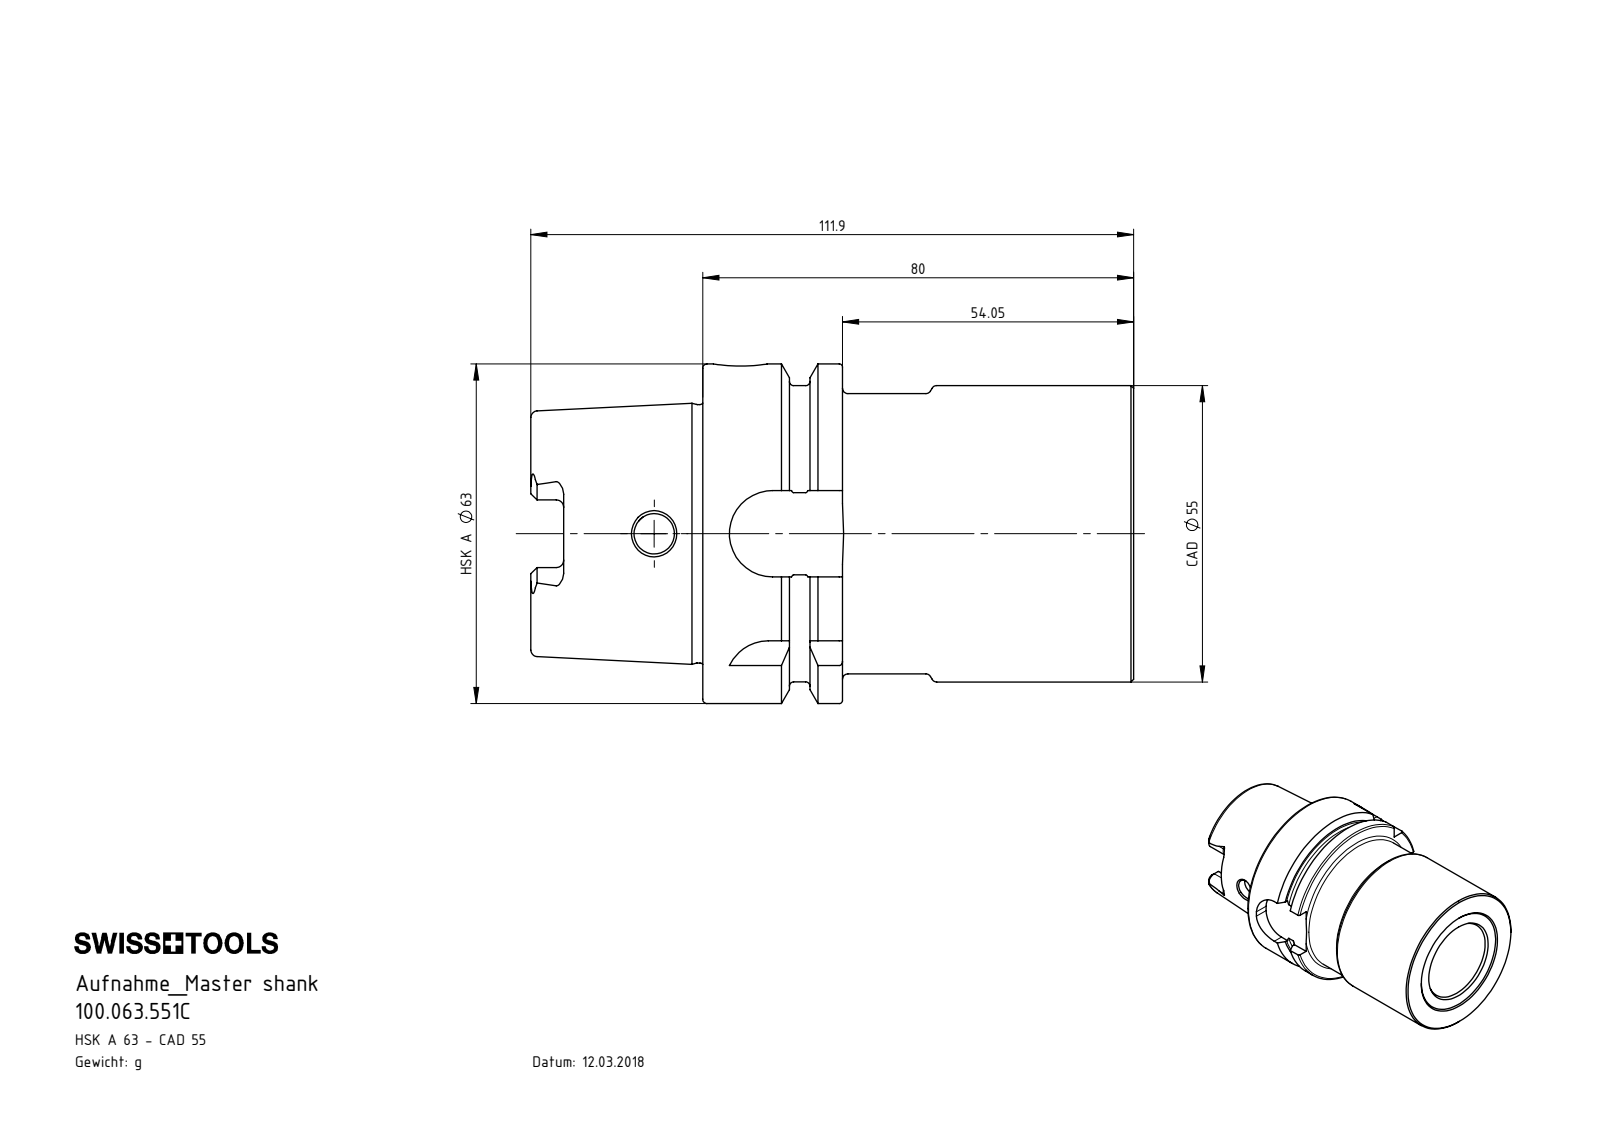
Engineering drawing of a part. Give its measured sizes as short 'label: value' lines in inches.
name: 100.063.551C
written by: SolidWorks 2017 (CONFIG_CONTROL_DESIGN)
unit: in
bodies: 1 solid, 202 faces (50 planar, 55 cylindrical, 97 other)
size: 4.406 × 2.48 × 2.48
volume: 10.46 in³; area: 56.4 in²
holes: 1× ⌀0.295, 1× ⌀0.331, 1× ⌀0.394, 1× ⌀0.669, 1× ⌀0.748, 1× ⌀0.965, 1× ⌀1.083, 1× ⌀1.181, 1× ⌀1.205, 1× ⌀1.339, 1× ⌀1.575
bosses: 1× ⌀2.48, 1× ⌀2.165, 1× ⌀2.163, 1× ⌀2.047, 1× ⌀1.887
rounds: 6× R0.055, 4× R0.113, 4× R0.315
face distances: 3.15, 1.022, 2.128, 0.63, 0.392, 2.758, 3.13, 2.738, 2.108, 0.02
